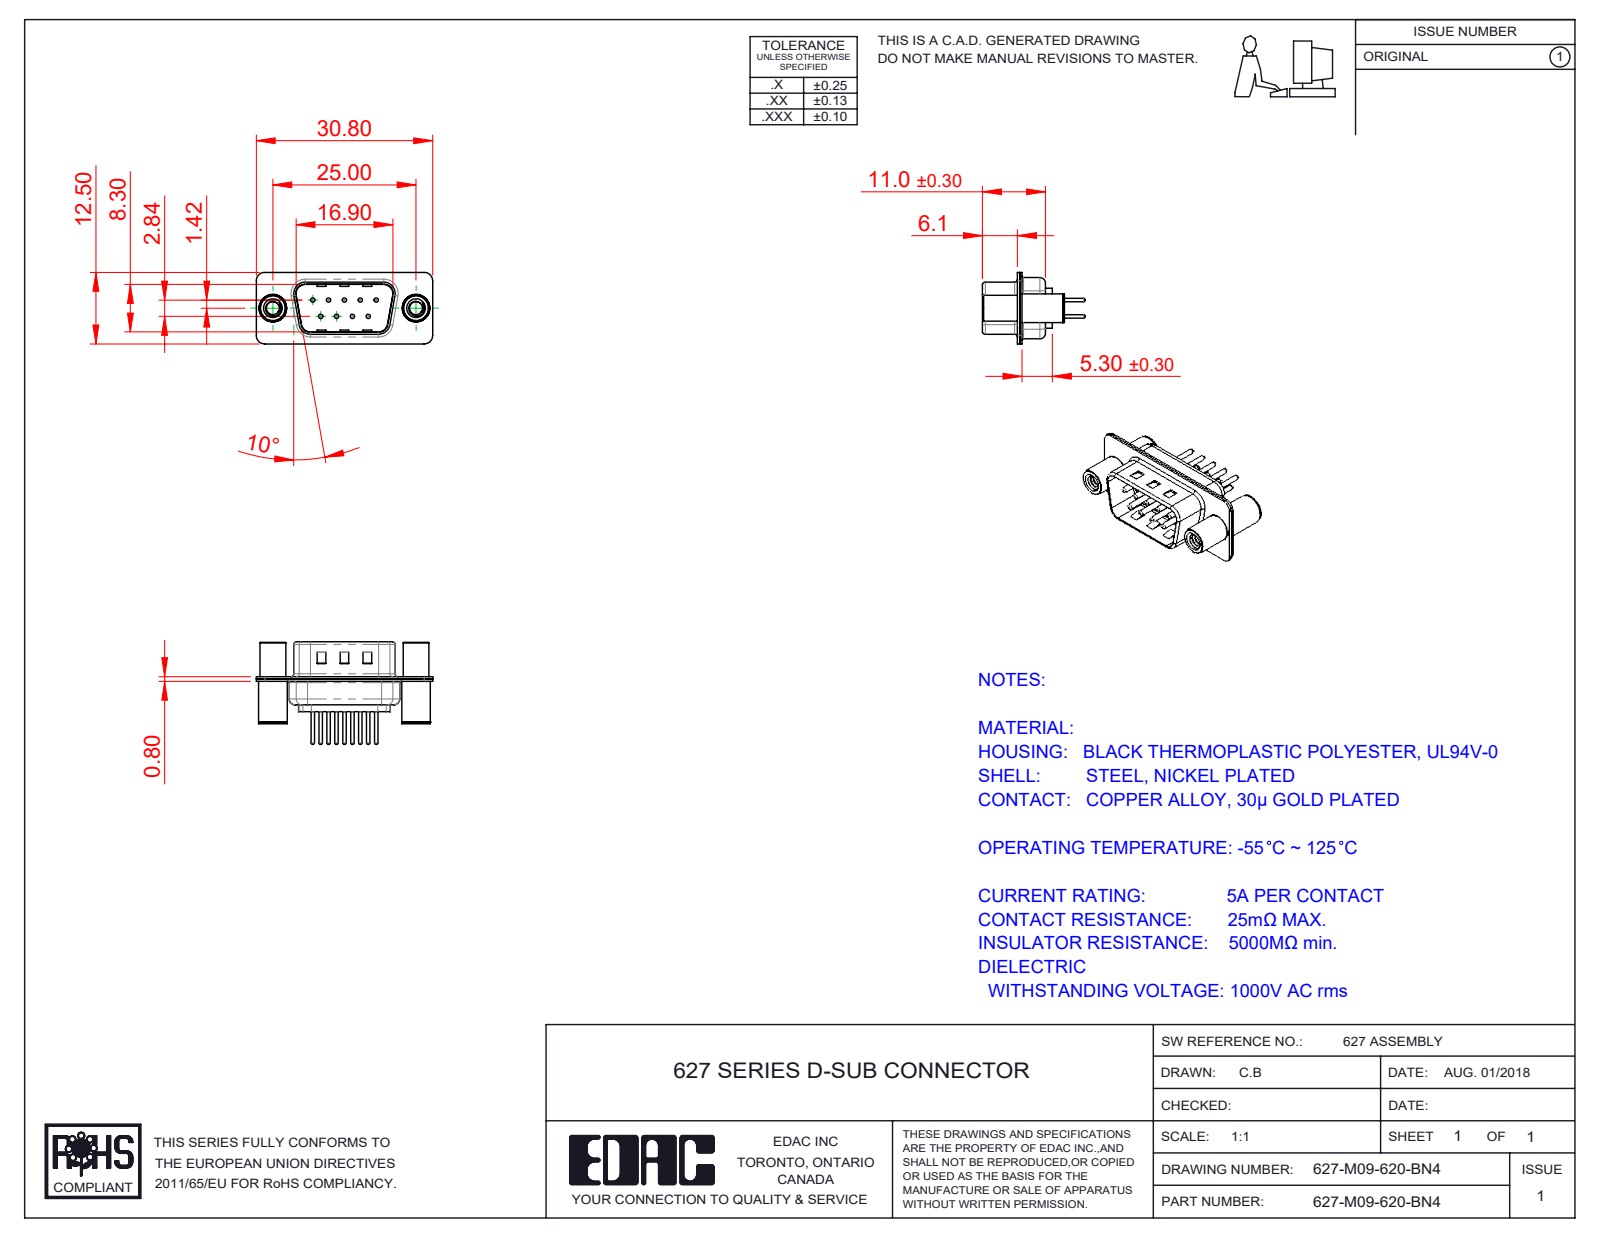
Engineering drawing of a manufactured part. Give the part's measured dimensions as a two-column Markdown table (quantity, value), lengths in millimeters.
| quantity | value |
| --- | --- |
| part name | 627M Contact Row 1_20; 627-M09-620-BN4; 627M Contact Row 2_20; 627M Housing_09 Contacts (+3 more) |
| STEP written by | SolidWorks 2020 (CONFIG_CONTROL_DESIGN) |
| units | millimeters |
| bodies | 14 solids, 723 faces (176 planar, 307 cylindrical, 240 other) |
| overall size | 30.8 × 17.9 × 12.5 |
| volume | 1 597 mm³ |
| surface area | 4 103 mm² |
| round holes (diameter × count) | 0.75 × 9, 1.6 × 9, 2 × 9, 2.26 × 2, 3.26 × 2, 4 × 2, 4.8 × 2 |
| round bosses / shafts (diameter × count) | 1.5 × 9, 0.6 × 9, 5 × 2, 4.9 × 2, 4.5 × 2 |
| partial cylindrical surfaces (radius × count) | 1.5 × 16, 2 × 12, 0.5 × 8, 1.6 × 8, 0.25 × 4, 0.6 × 4, 0.65 × 4, 0.9 × 4 |
| main face-to-face distances | 0.4, 0.8, 9.5, 9.1, 8.7, 0.65, 9.9, 1.2, 5.3, 6.1 |
| hole center spacings | 3.16, 2.77, 5.54, 5.03, 5.04, 8.31, 7.1, 7.48 |
